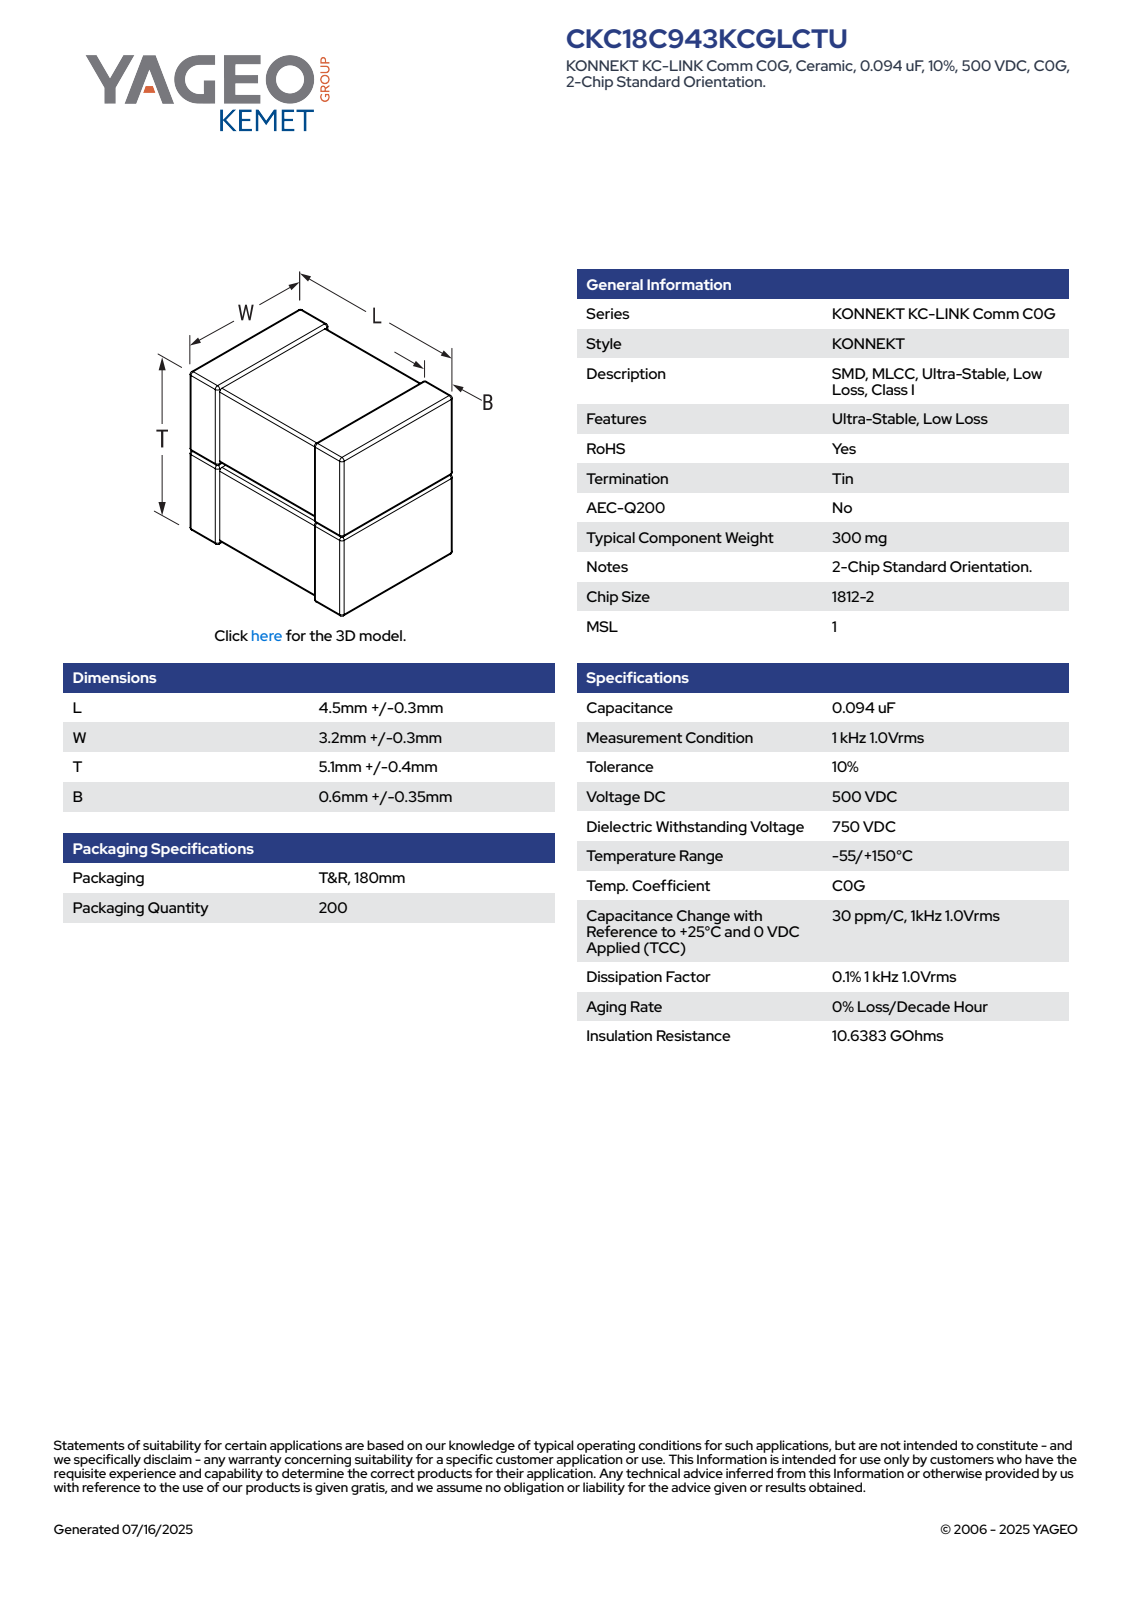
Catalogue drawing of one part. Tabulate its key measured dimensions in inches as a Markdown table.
| quantity | value |
| --- | --- |
| part name | CCSS_K2T_1812_L4.8W3.5B0.95T5.5 |
| STEP written by | SolidWorks 2020 (AUTOMOTIVE_DESIGN) |
| units | inches |
| bodies | 4 solids, 189 faces (81 planar, 76 cylindrical, 32 other) |
| overall size | 0.217 × 0.189 × 0.138 |
| volume | 0.005 in³ |
| surface area | 0.225 in² |
| main face-to-face distances | 0.103, 0.108, 0.189, 0.135, 0.132, 0.106, 0.111, 0.214, 0.211, 0.138 |
